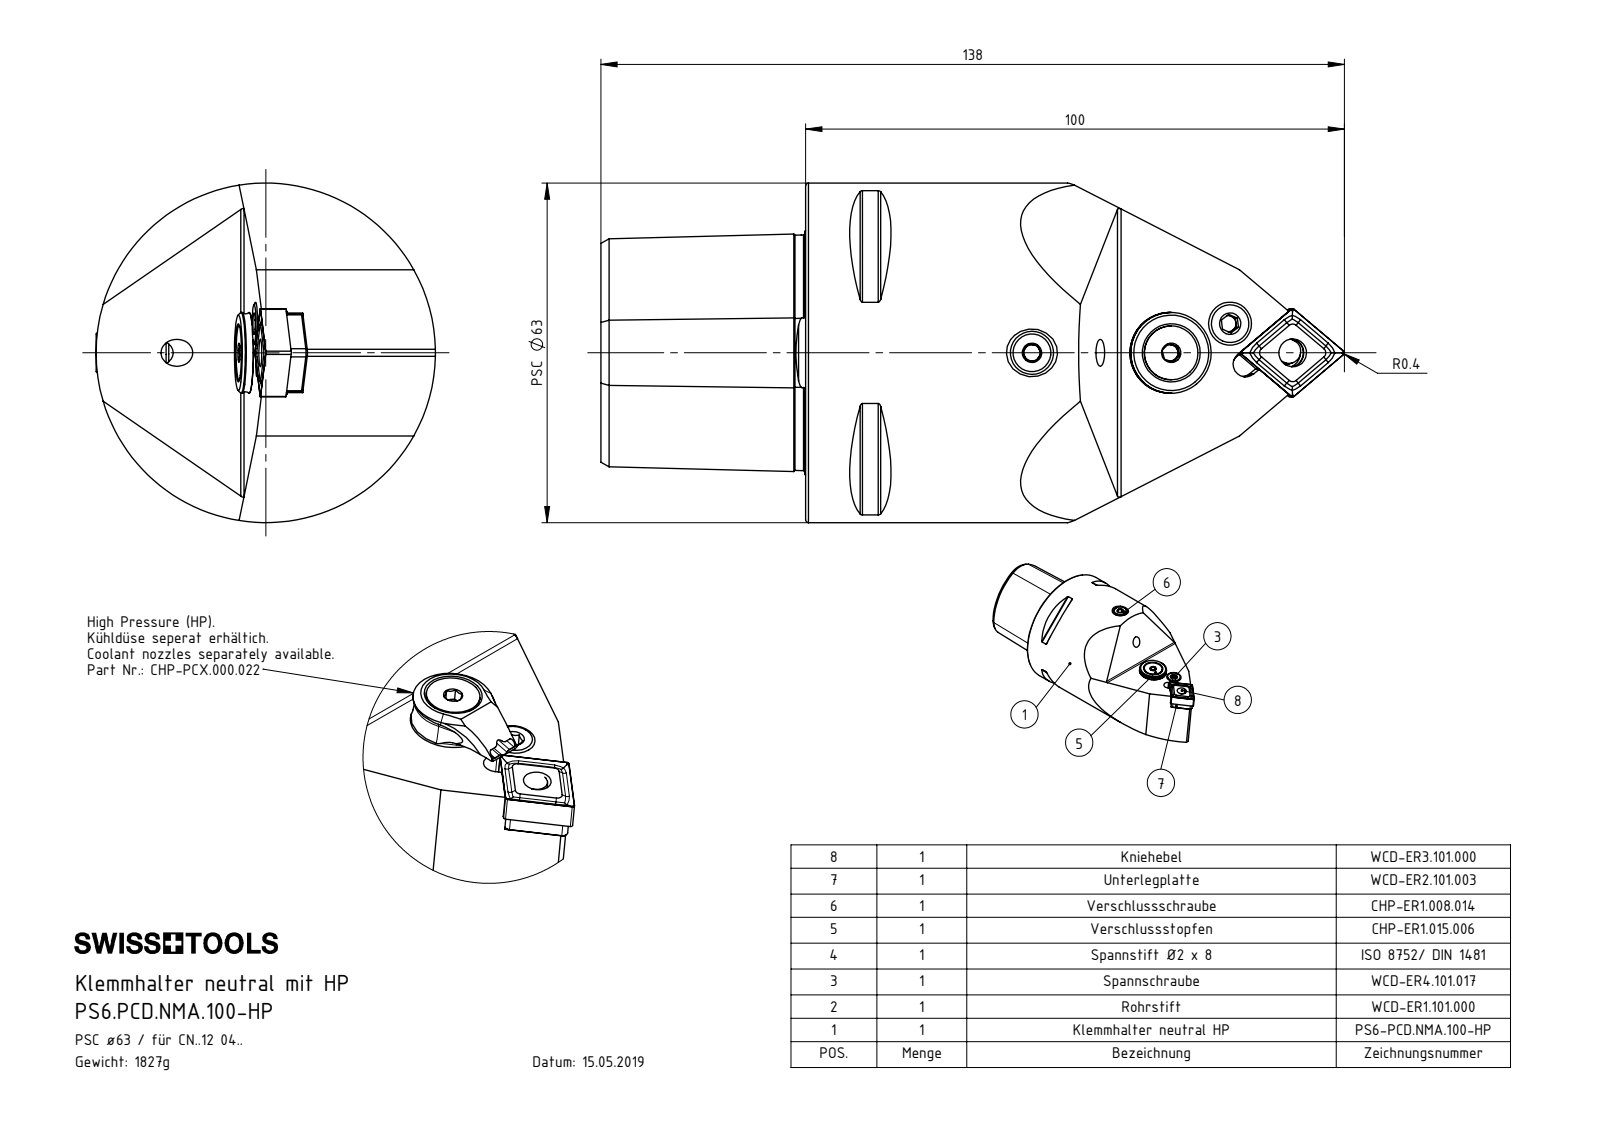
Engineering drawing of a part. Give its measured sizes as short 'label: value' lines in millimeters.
name: CHP-ER1.008.014_A; WCD-ER4.101.017_A; PS6.PCD.NMA.100-HP; WCD-ER3.101.000_A (+8 more)
written by: SolidWorks 2017 (AUTOMOTIVE_DESIGN)
unit: mm
bodies: 12 solids, 350 faces (145 planar, 77 cylindrical, 128 other)
size: 138 × 63 × 63
volume: 240 004 mm³; area: 38 593 mm²
holes: 2× ⌀4.2, 2× ⌀5, 2× ⌀7, 1× ⌀1.2, 1× ⌀2, 1× ⌀2.5, 1× ⌀3, 1× ⌀4, 1× ⌀5.16, 1× ⌀5.2, 1× ⌀6.4, 1× ⌀8.1
bosses: 2× ⌀8, 2× ⌀4.5, 1× ⌀63, 1× ⌀15, 1× ⌀13.4, 1× ⌀10, 1× ⌀7.9, 1× ⌀6.4
rounds: 10× R0.5, 4× R0.4, 4× R1, 3× R2.5, 2× R3.2, 1× R2.1, 1× R2.2, 1× R2.35
face distances: 38, 26.82, 24.88, 4.5, 27, 11, 4.45, 11.79, 55.8, 3.13
hole spacings: 4.51, 4.5, 4.53, 12.24, 12.25, 12.79, 12.85, 16.75
